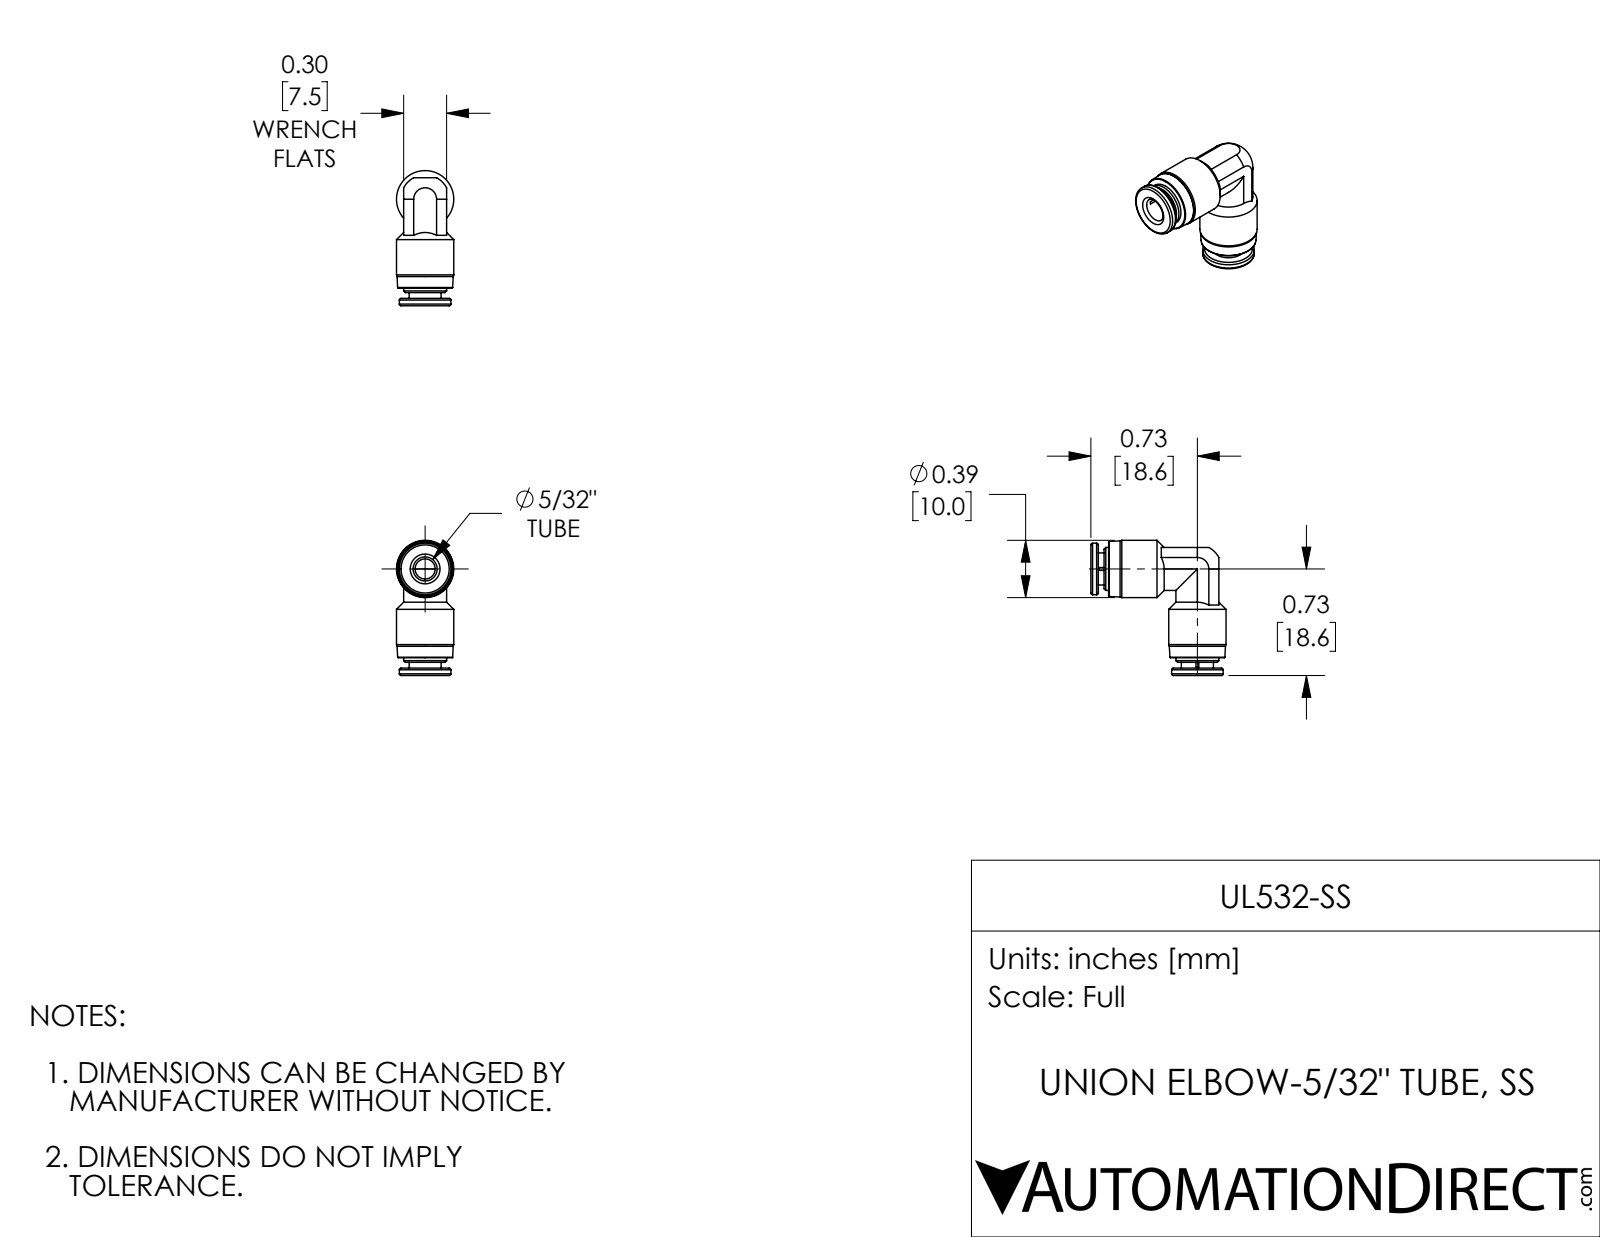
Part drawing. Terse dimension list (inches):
name: UL532-SS
written by: SolidWorks 2017 (AUTOMOTIVE_DESIGN)
unit: in
bodies: 1 solid, 104 faces (30 planar, 31 cylindrical, 43 other)
size: 0.929 × 0.929 × 0.394
volume: 0.11 in³; area: 2.847 in²
holes: 2× ⌀0.138, 2× ⌀0.165
bosses: 2× ⌀0.394, 2× ⌀0.354, 2× ⌀0.295, 2× ⌀0.22
rounds: 2× R0.167
face distances: 0.051, 0.829, 0.88, 0.758, 0.071, 0.122, 0.295, 0.789, 0.031, 0.039
